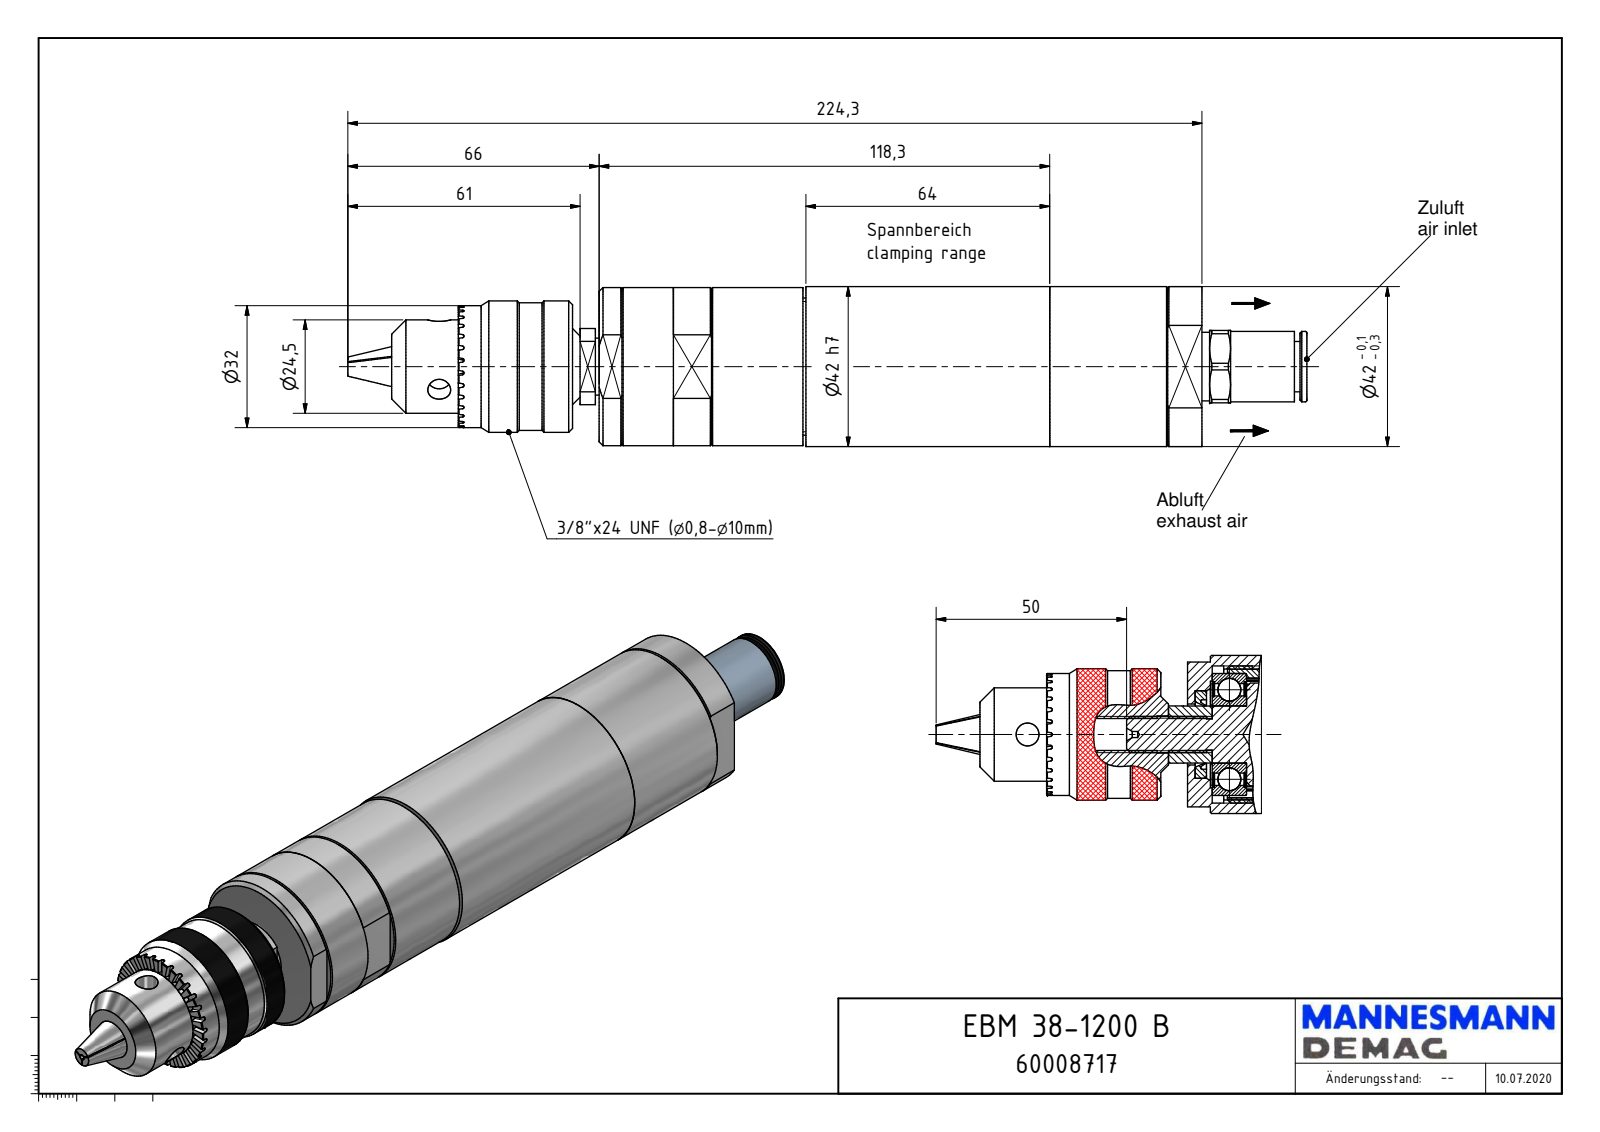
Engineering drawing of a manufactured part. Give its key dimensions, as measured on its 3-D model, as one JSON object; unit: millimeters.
{"part_name": "EBM 38-1200 B_60008717", "step_written_by": "Autodesk Inventor 2018 (AUTOMOTIVE_DESIGN)", "units": "millimeters", "bodies": {"solids": 1, "faces": 311, "planar": 173, "cylindrical": 66, "other": 72}, "overall_size": [251.25, 42, 42], "volume_mm3": 255913, "surface_area_mm2": 34814, "round_holes": [[6, 3], [1.5, 1], [12, 1], [16, 1], [23, 1]], "round_bosses_or_shafts": [[42, 1], [41.5, 1], [36, 1], [34.5, 1], [33.5, 1], [32, 1], [24.5, 1], [18.5, 1]], "partial_cylinders_radius": [[0.5, 23], [10, 1], [10.5, 1]], "face_to_face_distances": [157.7, 7, 37, 164.7, 1, 53.5, 60.7, 53.7, 104, 60.5]}
